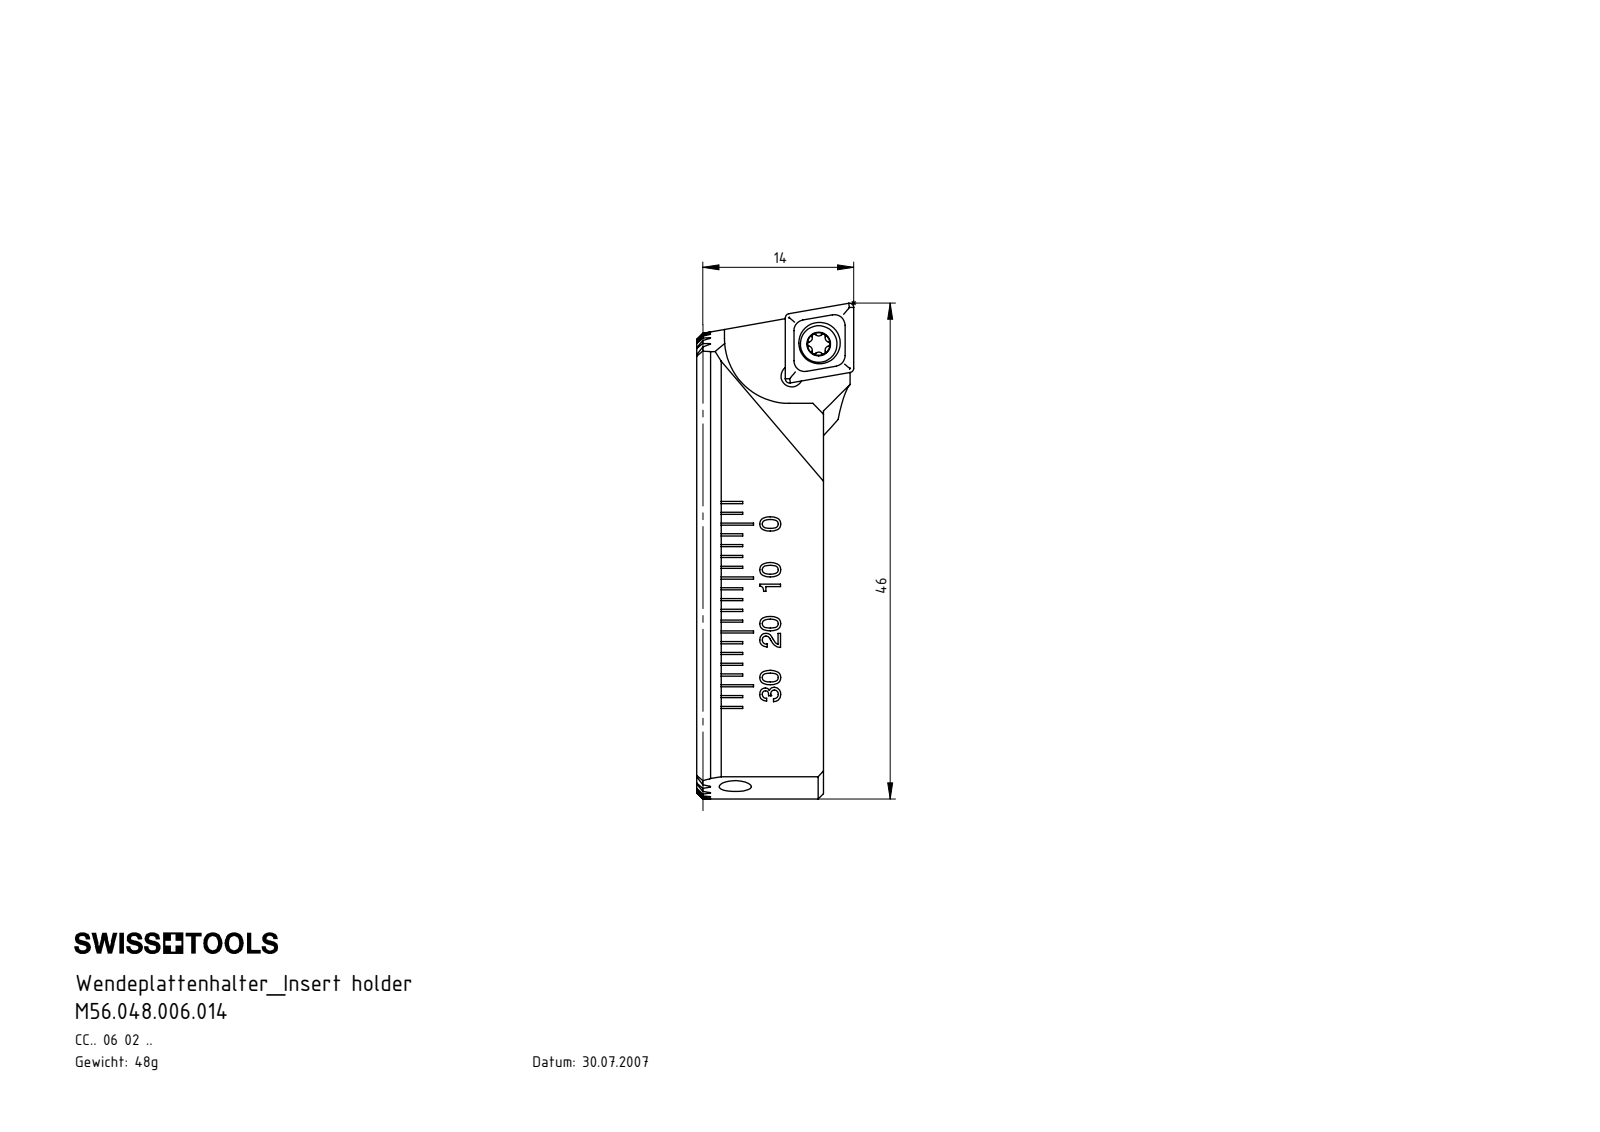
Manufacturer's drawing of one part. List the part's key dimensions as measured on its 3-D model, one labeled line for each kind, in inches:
Part name (STEP PRODUCT): CCMT060204; BV2-WCA.K11.014_B_mit beschriftung; KVT_MB_600_030; WCA-ER2.001.006_A (+1 more)
STEP written by: SolidWorks 2017 (AUTOMOTIVE_DESIGN)
Units: inches
Bodies: 5 solids, 411 faces (237 planar, 48 cylindrical, 126 other)
Overall size (bounding box): 1.811 × 0.732 × 0.574
Volume: 0.367 in³ · Surface area: 6.694 in²
Round holes (diameter × count): ⌀0.079 ×4, ⌀0.081 ×1, ⌀0.094 ×1, ⌀0.11 ×1, ⌀0.152 ×1
Round bosses / shafts (diameter × count): ⌀0.134 ×1, ⌀0.118 ×1, ⌀0.098 ×1
Partial cylindrical surfaces — rounded edges, fillets, slot ends (radius × count): R0.006 ×10, R0.008 ×6, R0.014 ×5, R0.106 ×2, R0.226 ×2, R0.014 ×1, R0.236 ×1, R0.866 ×1
Main face-to-face distances: 0.068, 0.136, 0.341, 0.409, 0.273, 0.732, 0.477, 0.472, 0.26, 0.205
Hole centre spacings: 0.153, 0.157
